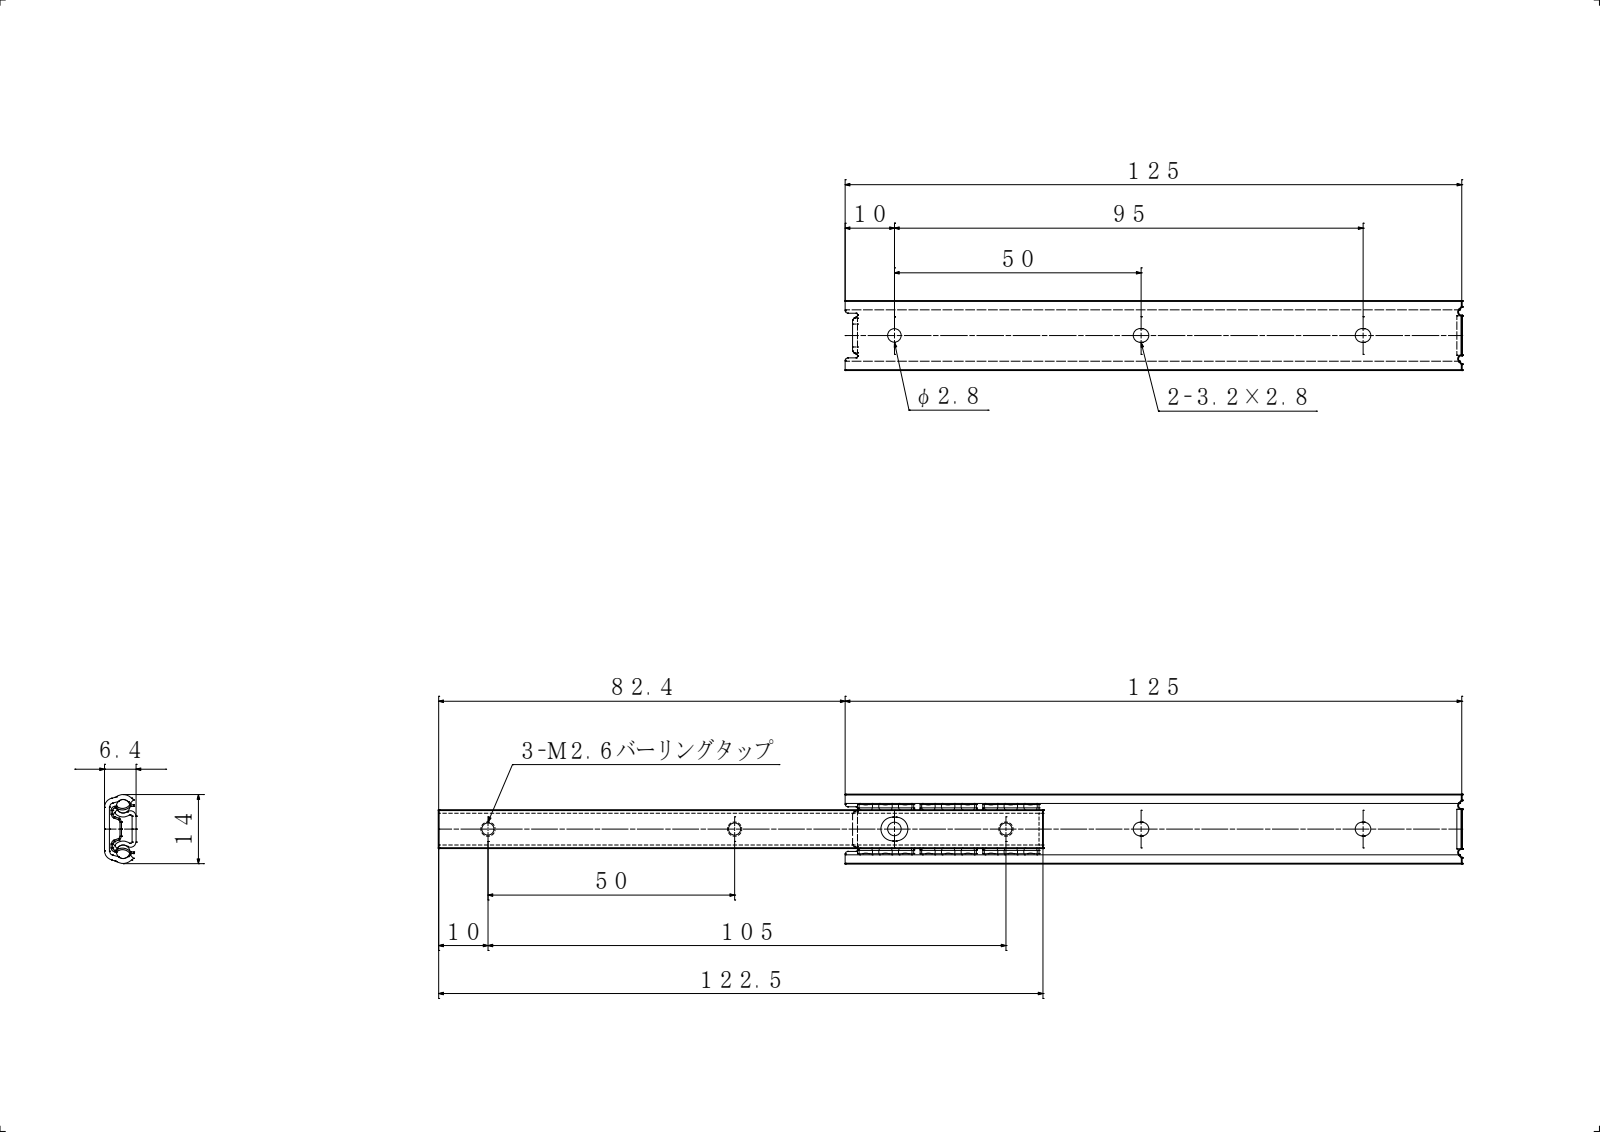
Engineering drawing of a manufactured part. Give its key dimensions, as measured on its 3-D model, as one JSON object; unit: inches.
{"part_name": "U1421-125; U1421-125 IM; U1421-125 OM", "step_written_by": "SolidWorks 2019 (CONFIG_CONTROL_DESIGN)", "units": "inches", "bodies": {"solids": 2, "faces": 187, "planar": 62, "cylindrical": 101, "other": 24}, "overall_size": [8.165, 0.551, 0.252], "volume_in3": 0.247, "surface_area_in2": 14.65, "round_holes": [[0.094, 3], [0.11, 1]], "round_bosses_or_shafts": [[0.134, 3]], "partial_cylinders_radius": [[0.02, 14], [0.012, 8], [0.018, 6], [0.039, 4], [0.043, 4], [0.055, 4], [0.031, 3], [0.004, 2]], "face_to_face_distances": [0.039, 0.031, 0.213, 0.252, 0.181, 0.22, 0.29, 0.33, 4.823, 3.303], "hole_center_spacings": [0.89, 1.276, 1.969, 2.165, 3.244, 4.134]}
